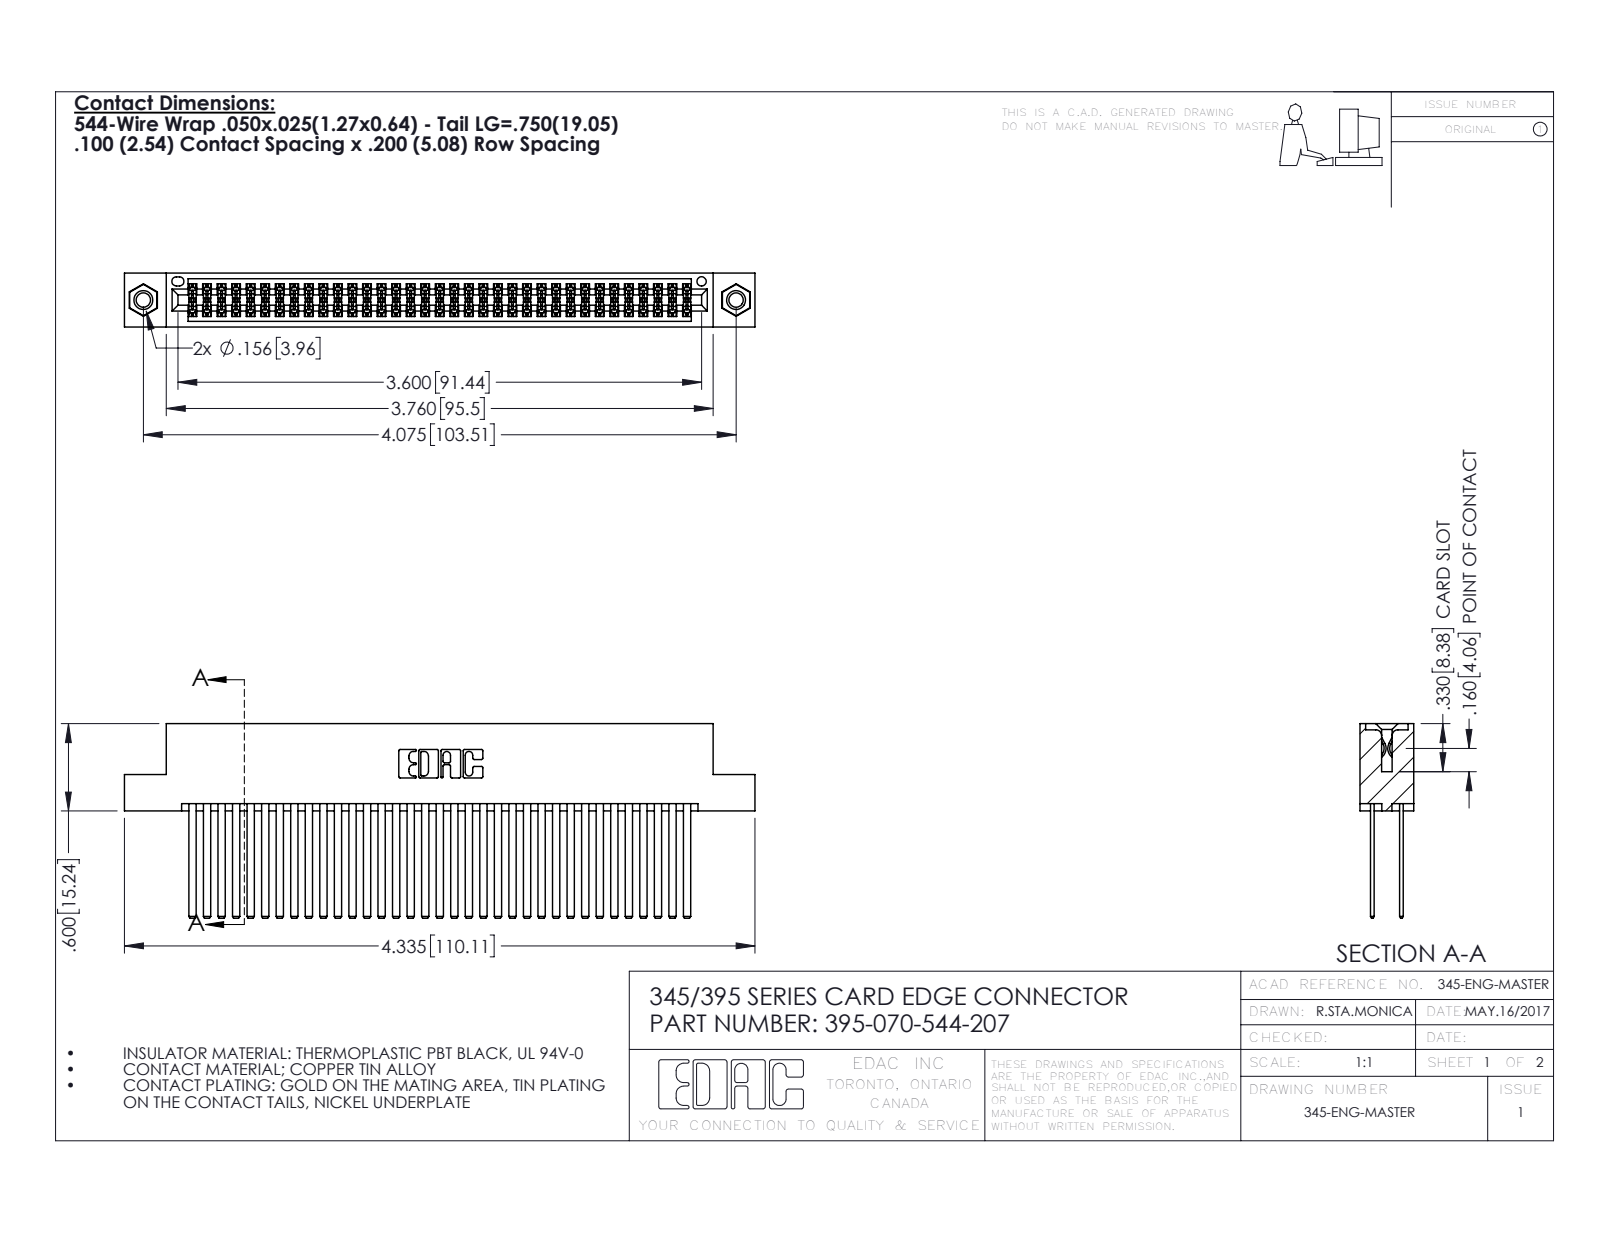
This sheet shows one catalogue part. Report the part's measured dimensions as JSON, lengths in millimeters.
{"part_name": "345 Part_Flush Mounting Lugs - 0.156 Dia-TI; 395-070-544-207; 345-292-001_345-293-144; 345-250-001_345-250-005-103", "step_written_by": "SolidWorks 2016 (CONFIG_CONTROL_DESIGN)", "units": "millimeters", "bodies": {"solids": 73, "faces": 3266, "planar": 2142, "cylindrical": 1108, "other": 16}, "overall_size": [110.1, 34, 9.4], "volume_mm3": 11600, "surface_area_mm2": 19920, "round_holes": [[2.5, 2], [3.2, 2], [4, 2], [1.6, 1]], "round_bosses_or_shafts": [[3.9, 2]], "partial_cylinders_radius": [[0.2, 105], [0.3, 22], [0.2, 6], [0.8, 6], [0.7, 3], [0.4, 2], [0.5, 2], [0.6, 2]], "face_to_face_distances": [5.1, 0.6, 1.8, 2.5, 6.9, 7.6, 5.7, 4.4, 9.4, 1.3], "hole_center_spacings": [6.9, 97.5, 103.5]}
